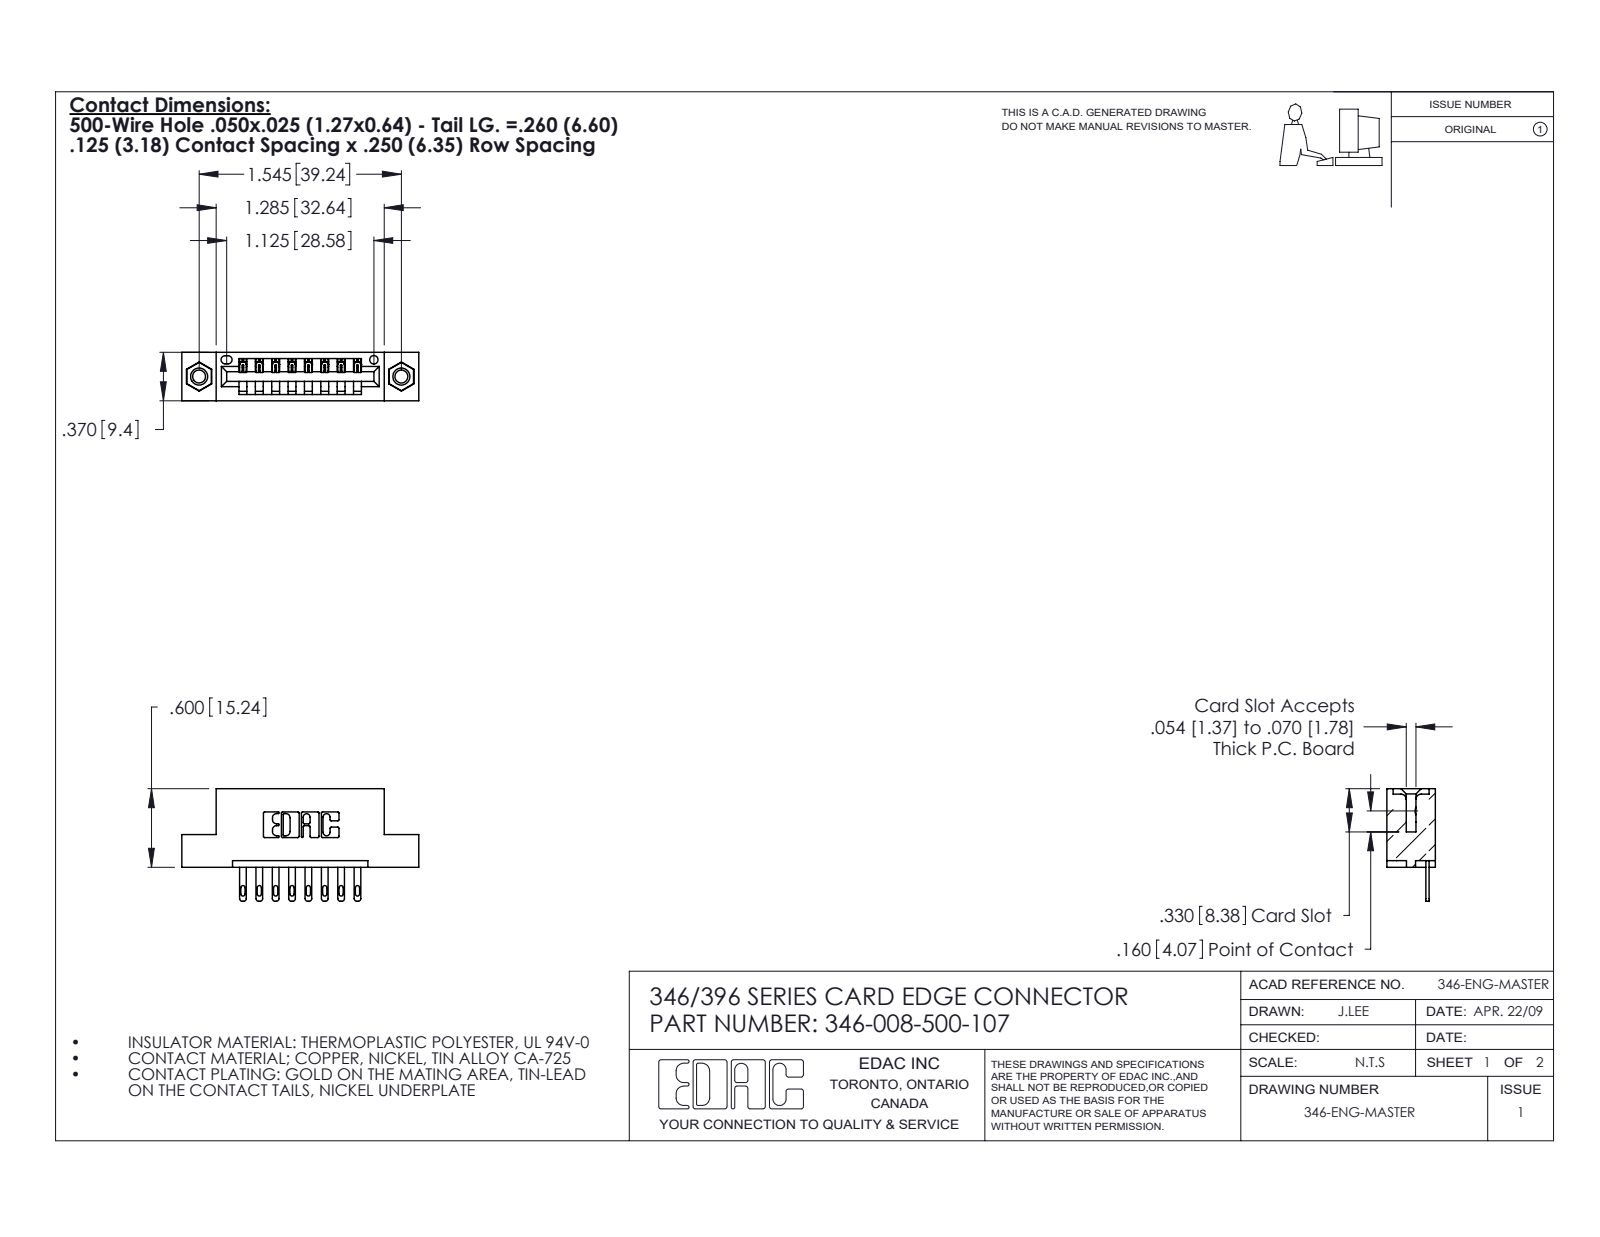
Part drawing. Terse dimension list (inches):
name: 346-008-500-107; 345-292-001_345-293-100; 346 Part_Flush Mounting Lugs - 0.156 Dia-TI; 345-250-001_345-250-005-103
written by: SolidWorks 2020 (CONFIG_CONTROL_DESIGN)
unit: in
bodies: 11 solids, 614 faces (380 planar, 218 cylindrical, 16 other)
size: 1.81 × 0.86 × 0.37
volume: 0.254 in³; area: 7.569 in²
holes: 2× ⌀0.098, 2× ⌀0.125, 2× ⌀0.156, 1× ⌀0.064
bosses: 2× ⌀0.155
rounds: 22× R0.01, 16× R0.006, 16× R0.016, 16× R0.02, 6× R0.007, 6× R0.031, 3× R0.026, 2× R0.031
face distances: 0.25, 0.37, 0.048, 0.322, 0.5, 0.072, 0.298, 0.025, 0.148, 0.222
hole spacings: 0.246, 1.341, 1.545
